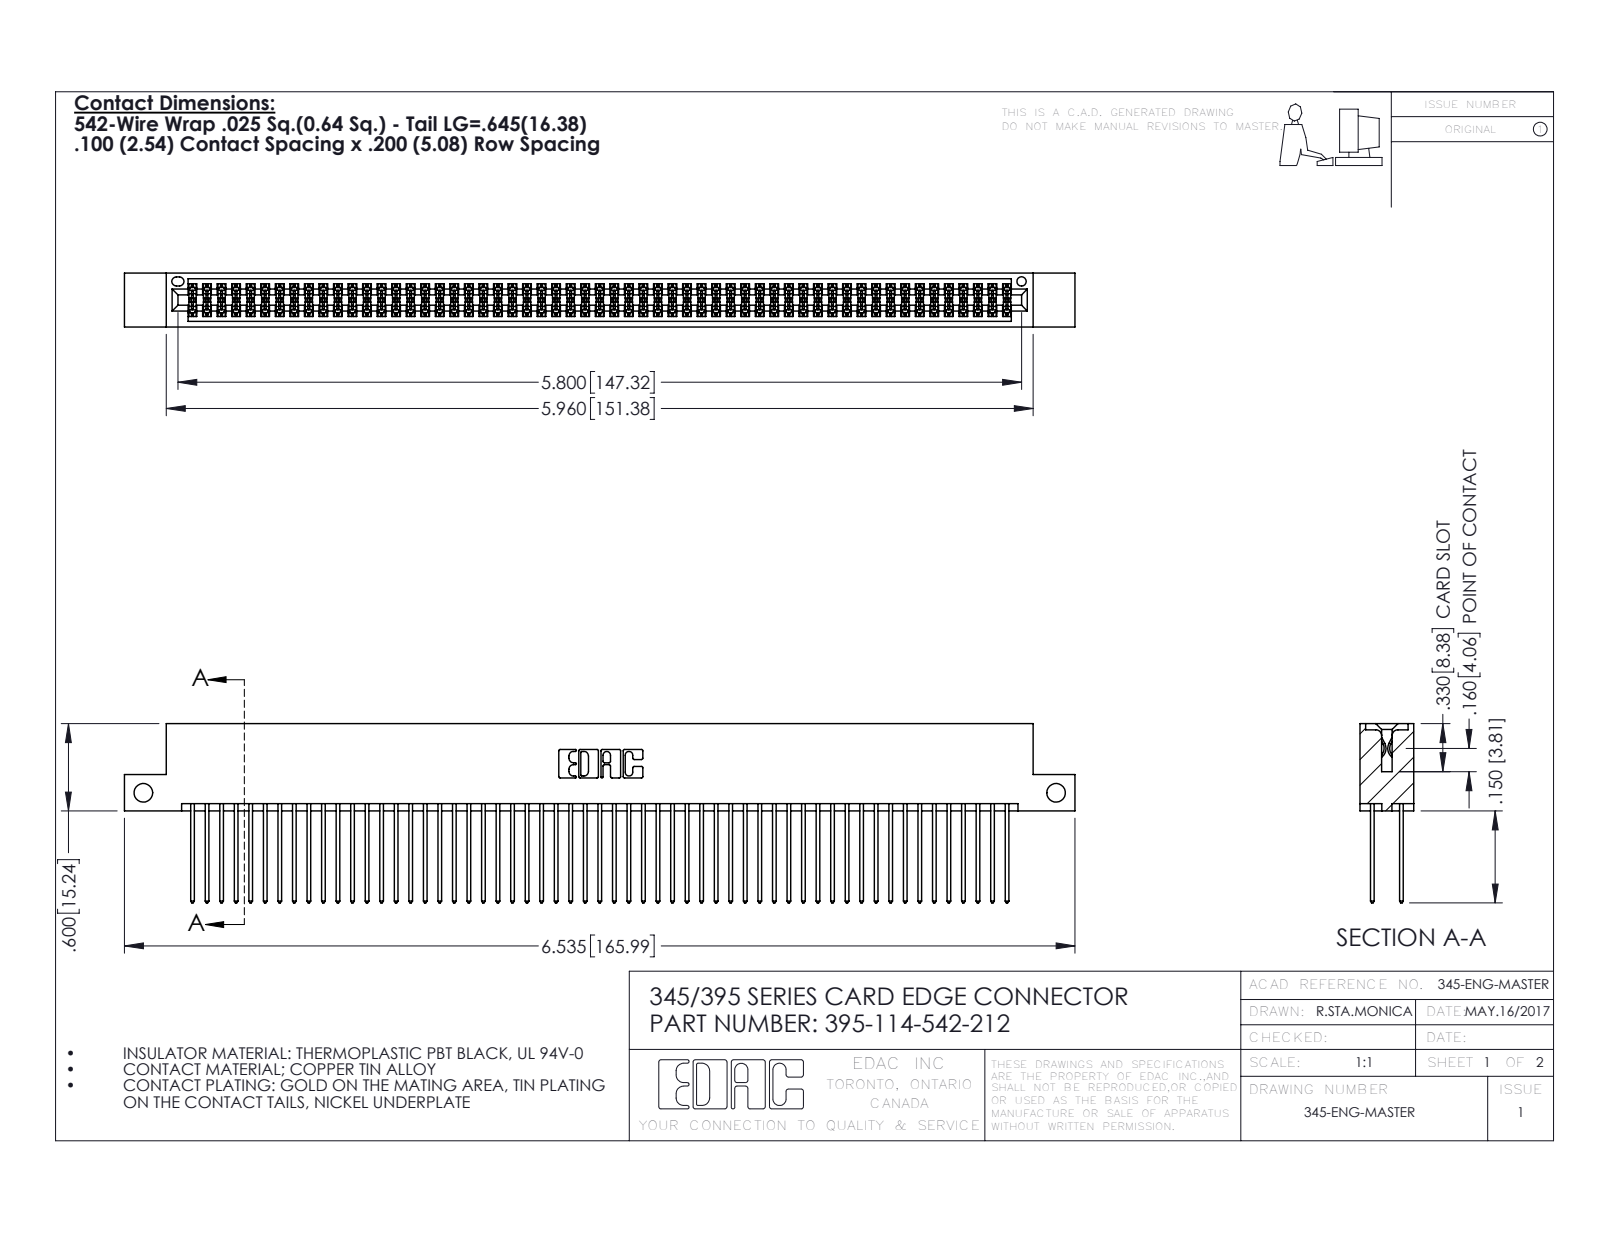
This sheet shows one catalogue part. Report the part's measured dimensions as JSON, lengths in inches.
{"part_name": "345 Part_Flush Mounting Lugs - Side Mount; 395-114-542-212; 345-292-001_345-293-142", "step_written_by": "SolidWorks 2016 (CONFIG_CONTROL_DESIGN)", "units": "inches", "bodies": {"solids": 115, "faces": 5826, "planar": 3842, "cylindrical": 1984, "other": 0}, "overall_size": [6.535, 1.232, 0.37], "volume_in3": 1.02, "surface_area_in2": 42.37, "round_holes": [[0.128, 2], [0.064, 1]], "partial_cylinders_radius": [[0.006, 171], [0.01, 114], [0.01, 22], [0.007, 6], [0.031, 6], [0.026, 3], [0.014, 2], [0.019, 2]], "face_to_face_distances": [0.298, 0.072, 0.2, 0.098, 0.272, 0.025, 0.225, 0.37, 0.175, 0.149], "hole_center_spacings": [6.275]}
